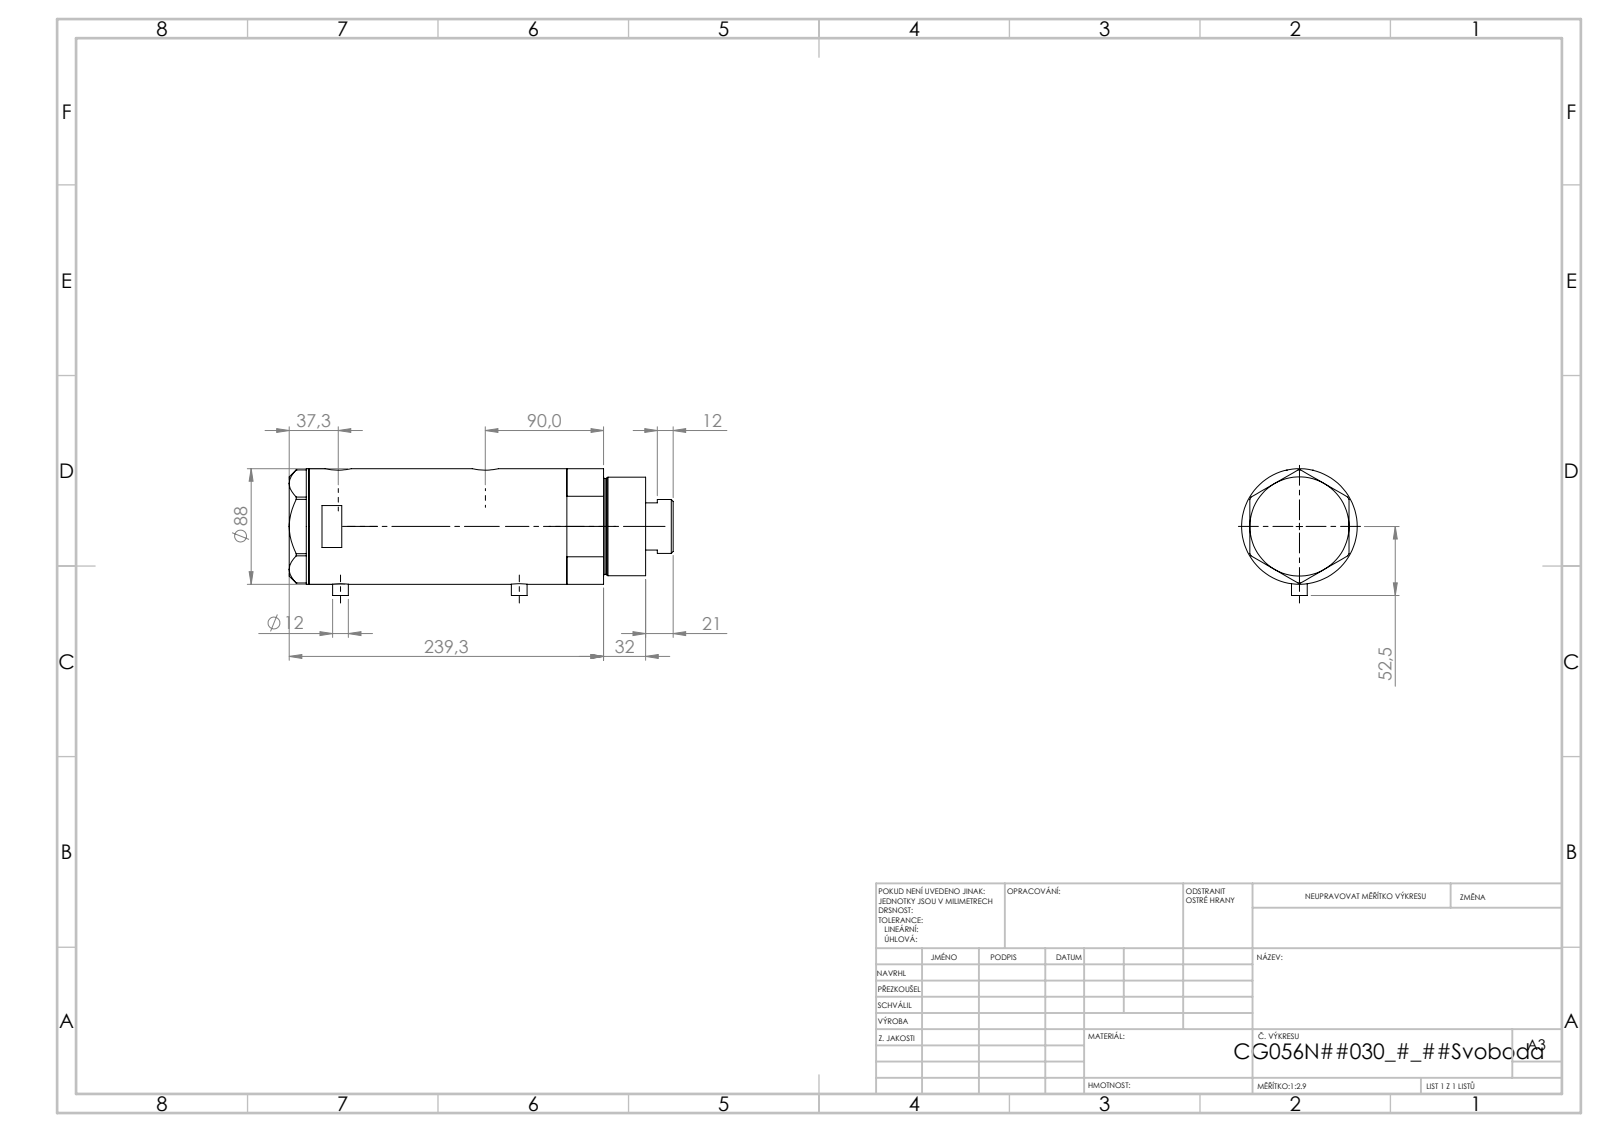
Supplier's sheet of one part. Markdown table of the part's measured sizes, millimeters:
| quantity | value |
| --- | --- |
| part name | V270CG_BACK; V270CG_MIDDLE; V270CG_FRONT; V270CG_VC |
| STEP written by | SolidWorks 2019 (CONFIG_CONTROL_DESIGN) |
| units | millimeters |
| bodies | 4 solids, 126 faces (53 planar, 53 cylindrical, 20 other) |
| overall size | 292.25 × 96.5 × 88 |
| volume | 1 550 000 mm³ |
| surface area | 222 426 mm² |
| round holes (diameter × count) | 5 × 2, 12.5 × 2, 13.16 × 2, 20 × 2, 14.5 × 1, 42 × 1, 43.5 × 1, 56 × 1, 60 × 1, 80 × 1 |
| round bosses / shafts (diameter × count) | 12 × 2, 88 × 1, 75 × 1, 73 × 1, 41 × 1 |
| main face-to-face distances | 134.4, 26, 108.4, 15, 41, 149.4, 256.3, 271.3, 230.3, 121.9 |
| hole center spacings | 1.7, 25.8, 110.3, 112, 136.1, 137.8 |
